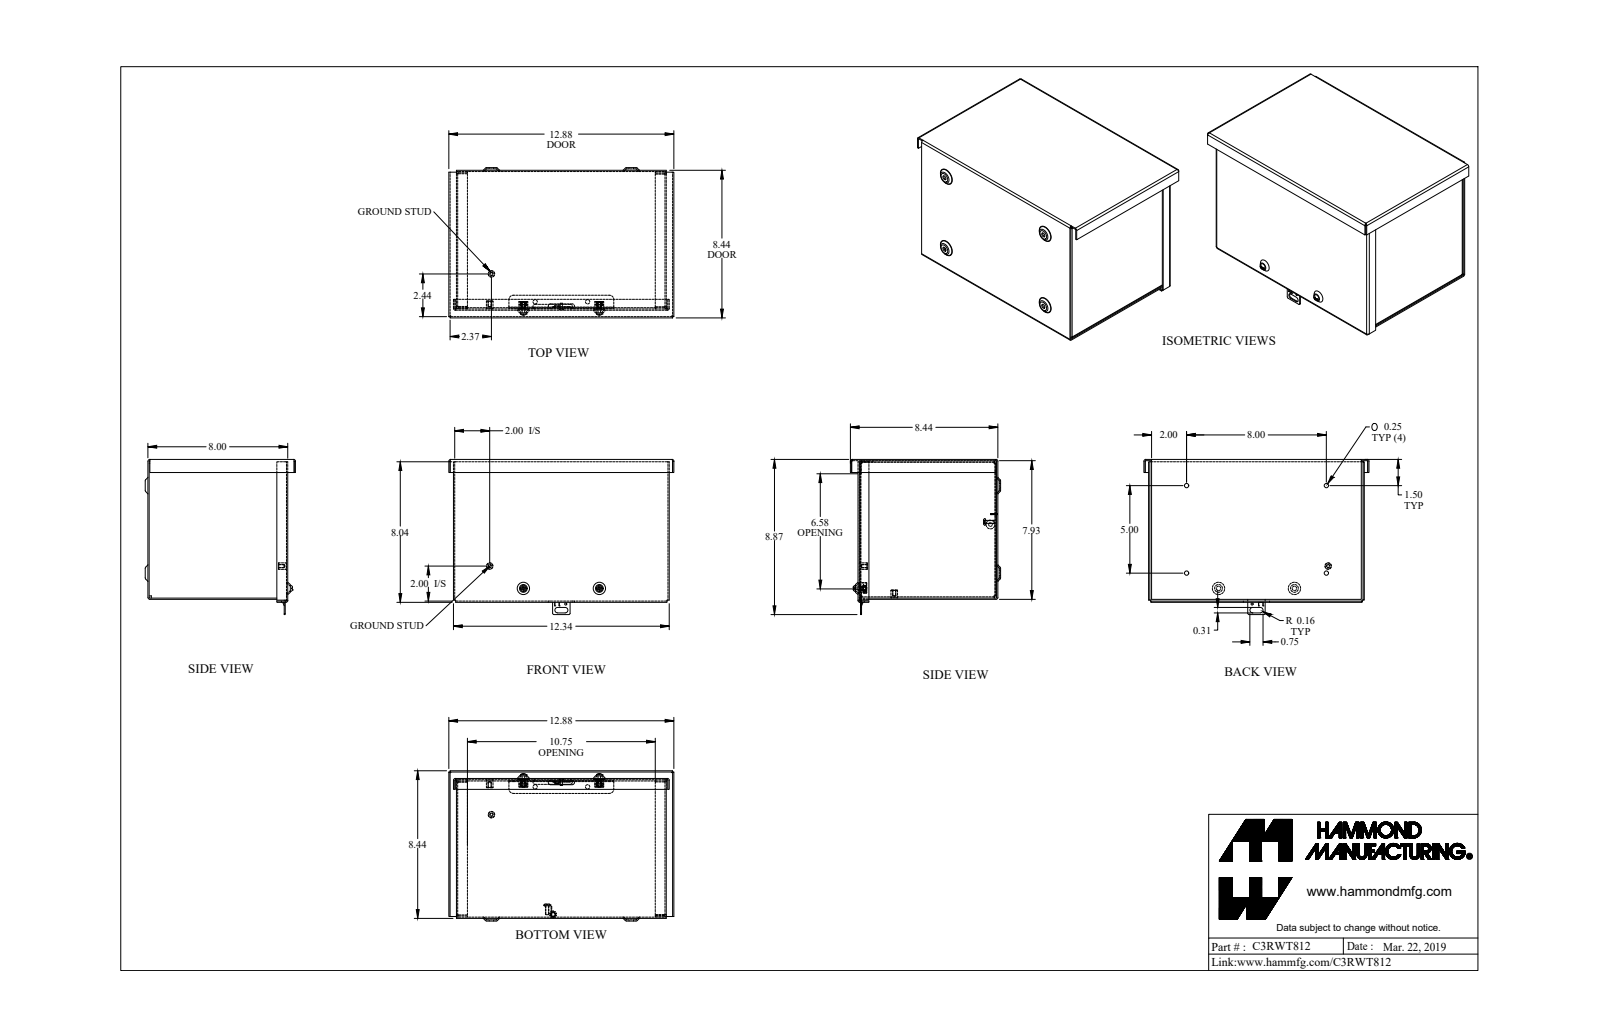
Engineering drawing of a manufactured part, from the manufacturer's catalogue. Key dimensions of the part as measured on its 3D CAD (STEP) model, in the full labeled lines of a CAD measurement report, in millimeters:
Part name (STEP PRODUCT): C3RWT812_Default
STEP written by: SolidWorks 2019 (CONFIG_CONTROL_DESIGN)
Units: millimetres
Bodies: 19 solids, 643 faces (344 planar, 199 cylindrical, 100 other)
Overall size (bounding box): 342.9 × 225.3 × 218.3
Volume: 717 300 mm³ · Surface area: 797 400 mm²
Round holes (diameter × count): ⌀6.4 ×6, ⌀4 ×4, ⌀5.2 ×2, ⌀5.4 ×2, ⌀5.8 ×2, ⌀3.2 ×1, ⌀3.5 ×1, ⌀5.1 ×1, ⌀5.5 ×1
Round bosses / shafts (diameter × count): ⌀4.8 ×3, ⌀9.5 ×2, ⌀3.8 ×2, ⌀12.7 ×1, ⌀9.3 ×1, ⌀5.3 ×1, ⌀3.9 ×1, ⌀3.2 ×1
Partial cylindrical surfaces — rounded edges, fillets, slot ends (radius × count): R0.9 ×18, R2.7 ×18, R3.2 ×10, R2 ×8, R2.7 ×8, R6.4 ×6, R0.4 ×4, R0.6 ×4
Main face-to-face distances: 1.8, 201.4, 199.5, 203.2, 303, 304.8, 301.1, 2.3, 199, 197.2
Hole centre spacings: 90.3, 274.9, 55.3, 158.3, 237.1, 51.5, 53.8, 105
